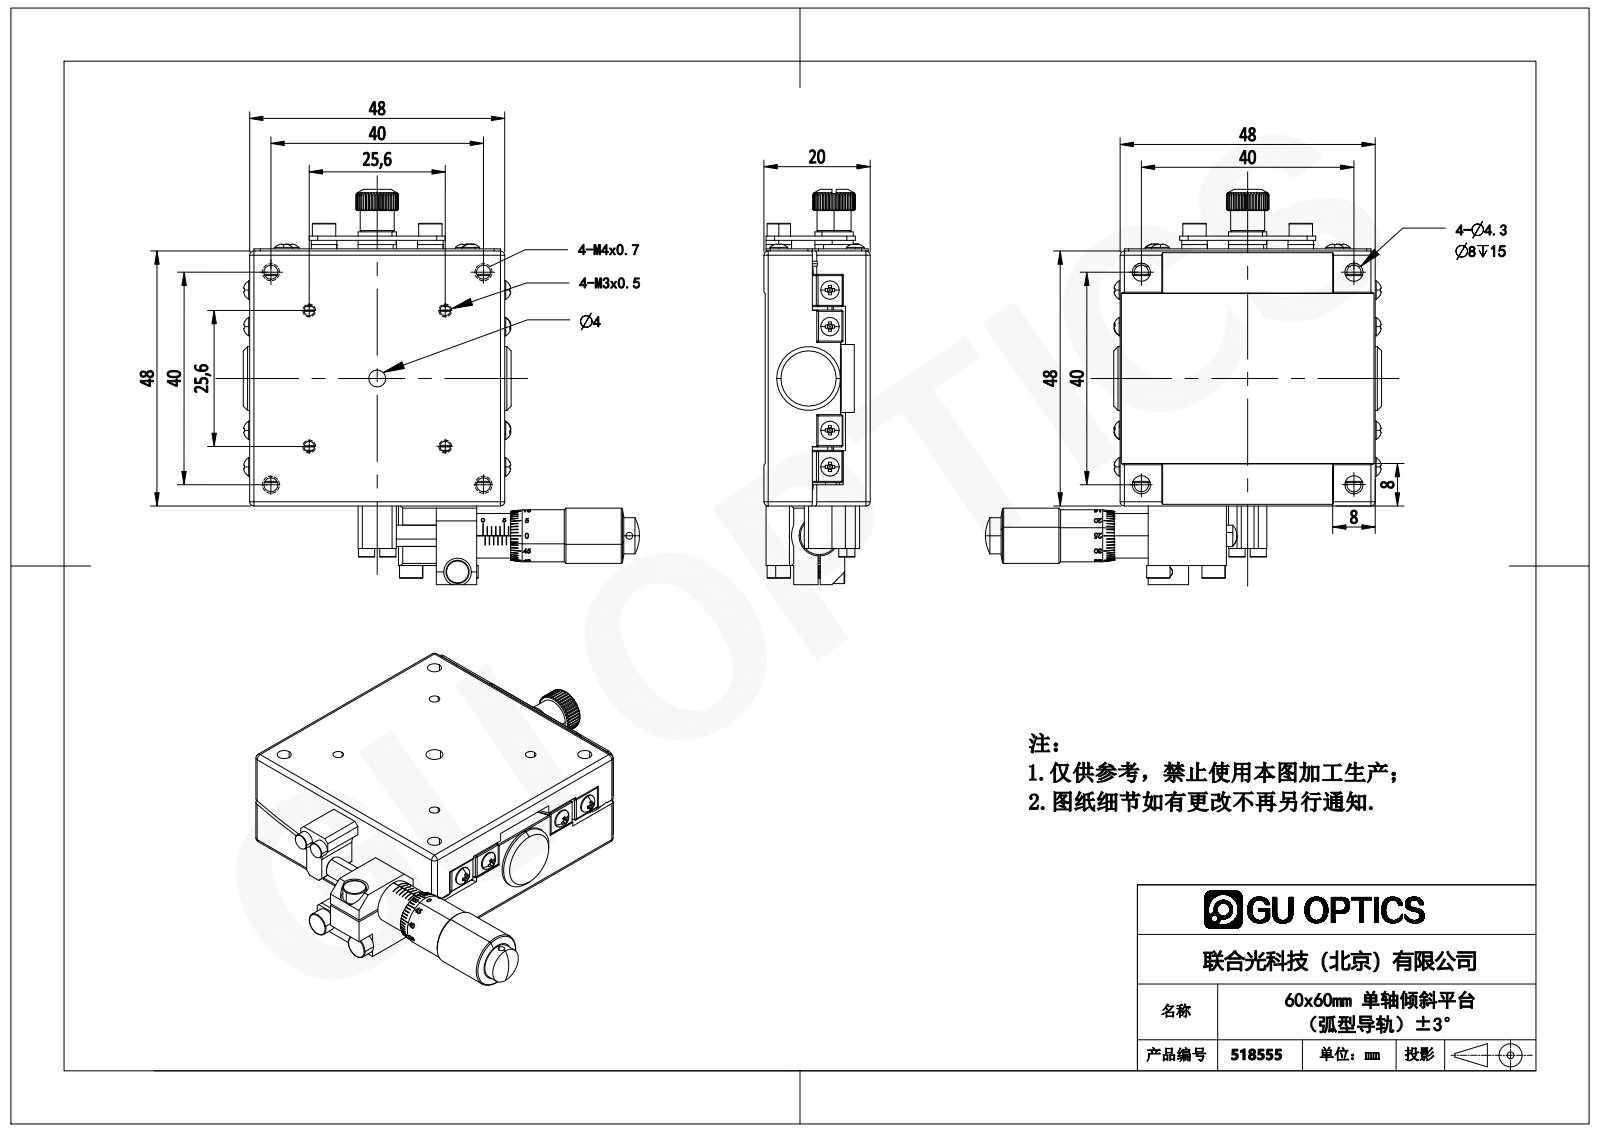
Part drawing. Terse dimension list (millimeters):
name: MXG6-100VM
written by: SolidWorks 2020 (CONFIG_CONTROL_DESIGN)
unit: mm
bodies: 2 solids, 1498 faces (907 planar, 357 cylindrical, 234 other)
size: 93.2 × 93 × 25
volume: 85 133 mm³; area: 34 553 mm²
holes: 5× ⌀2.5, 4× ⌀3.3, 4× ⌀4.3, 4× ⌀8, 1× ⌀1.6, 1× ⌀3.4, 1× ⌀3.8, 1× ⌀4, 1× ⌀6.5, 1× ⌀9.5, 1× ⌀10.7, 1× ⌀12.5
bosses: 5× ⌀5.5, 4× ⌀4.35, 4× ⌀4.2, 2× ⌀6, 2× ⌀3.8, 1× ⌀15, 1× ⌀13, 1× ⌀12.25
rounds: 16× R1, 12× R2, 4× R1.5, 2× R2.25, 2× R3.5, 2× R5.5, 1× R5, 1× R106.25
face distances: 24.7, 60.5, 60, 0.5, 33, 24.8, 5, 7.6, 8.4, 55
hole spacings: 41.98, 12.73, 22.63, 32, 35.36, 50, 57.98, 70.71
